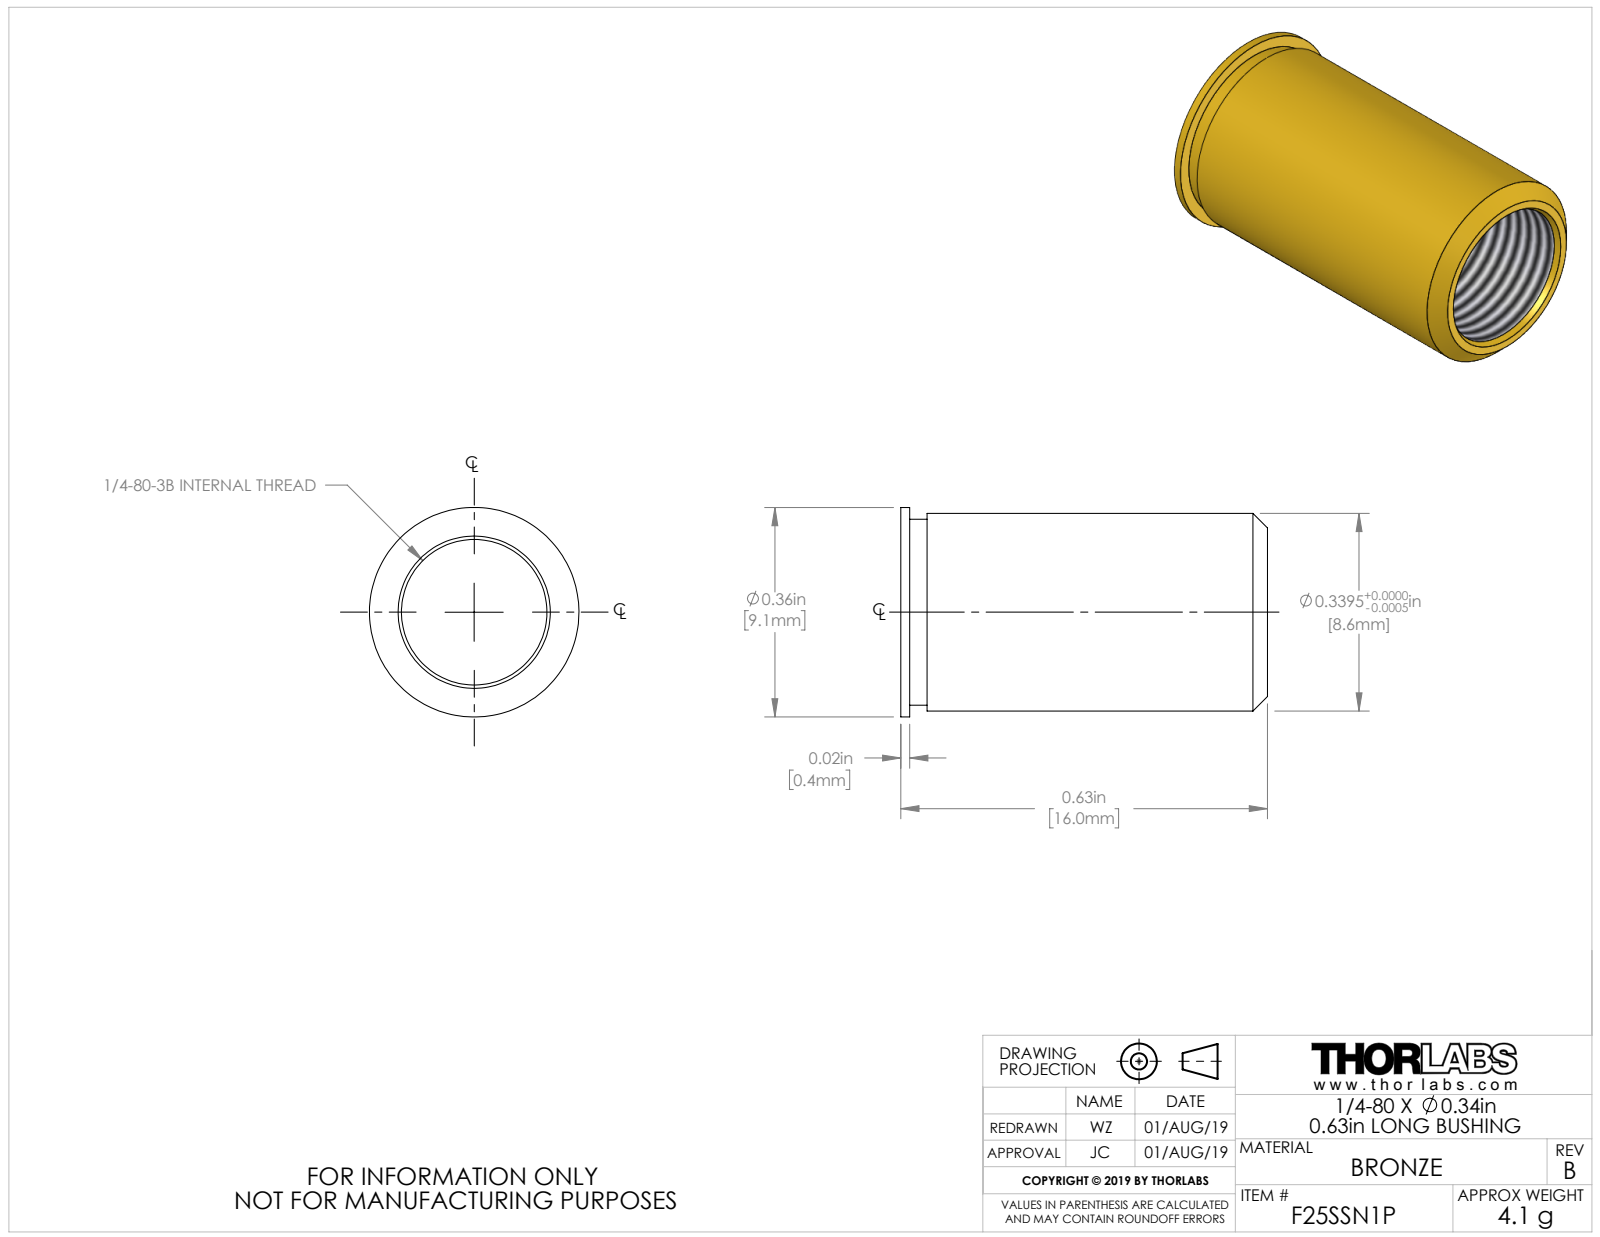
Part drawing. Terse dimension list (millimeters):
name: 18991-E0W
written by: SolidWorks 2007 (AUTOMOTIVE_DESIGN)
unit: mm
bodies: 1 solid, 18 faces (4 planar, 8 cylindrical, 6 other)
size: 16 × 9.14 × 9.14
volume: 420 mm³; area: 819 mm²
holes: 1× ⌀6.35
bosses: 1× ⌀9.14, 1× ⌀8.62, 1× ⌀8.12
face distances: 0.38, 16, 15.62, 1.14, 0.76, 14.86
